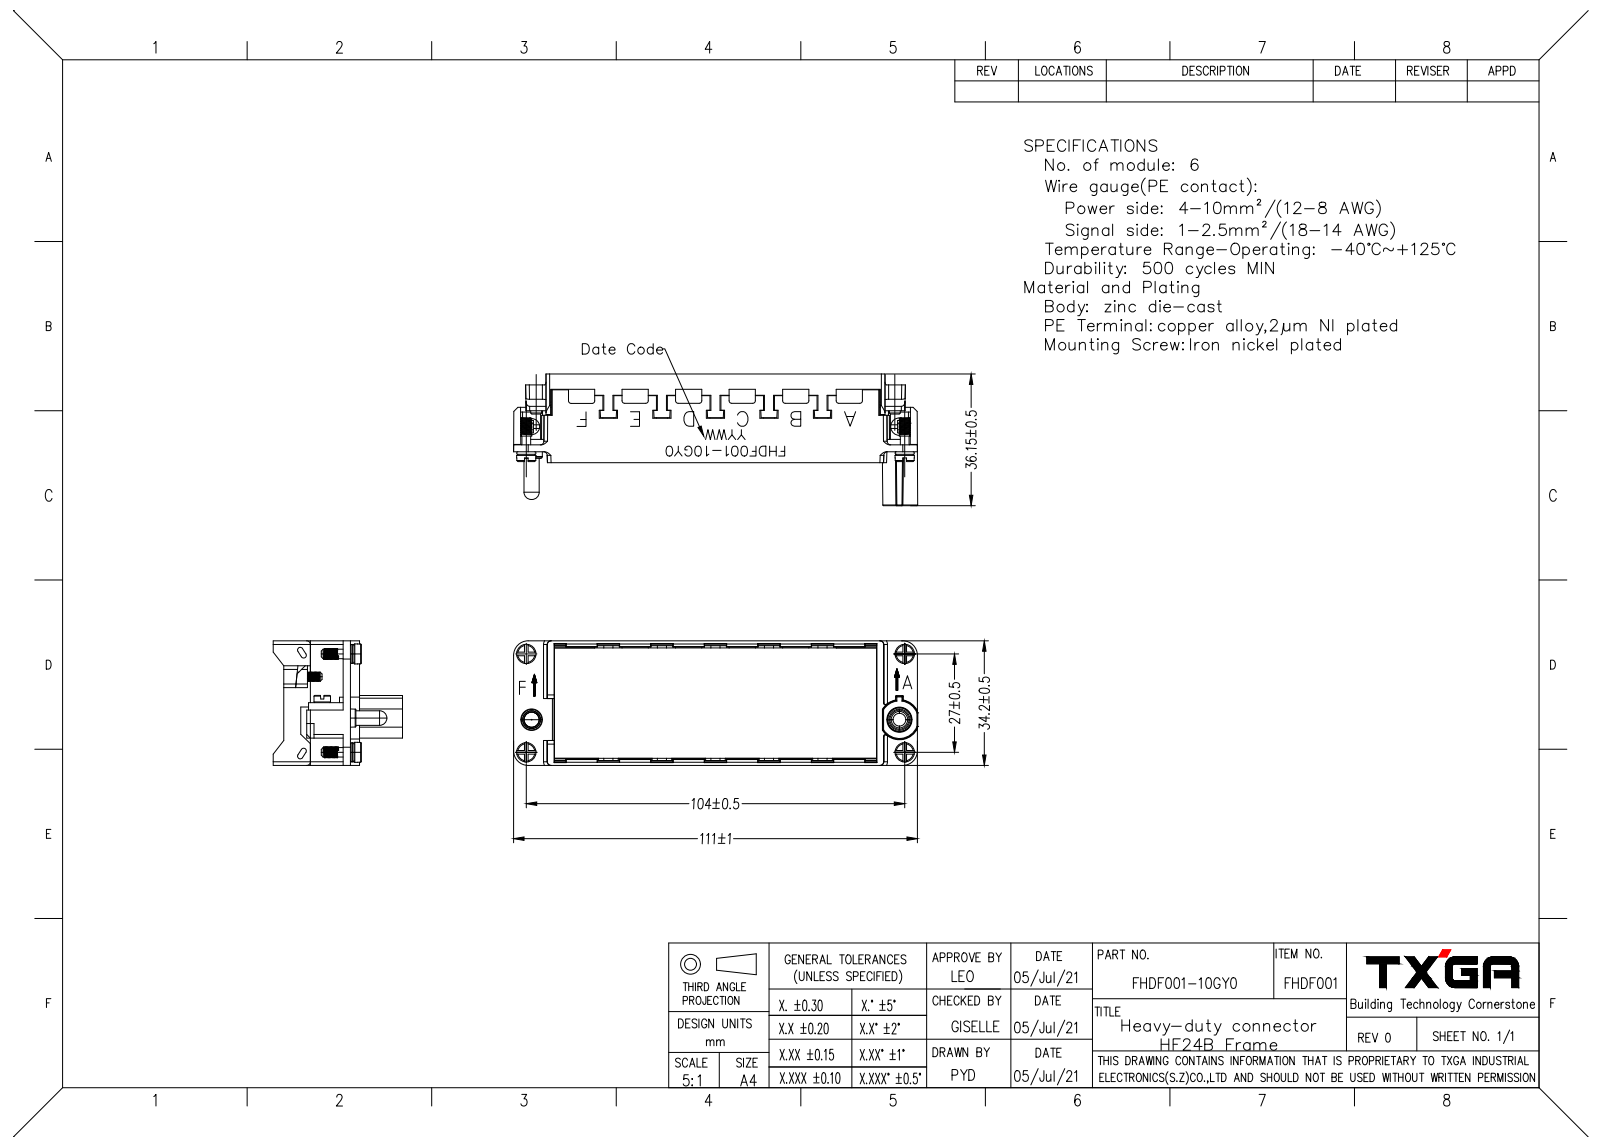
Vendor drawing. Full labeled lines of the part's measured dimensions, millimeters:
Part name (STEP PRODUCT): FHDF001-10NA0 HF24B-NUA-REF（渲染）
STEP written by: SolidWorks 2021 (CONFIG_CONTROL_DESIGN)
Units: millimetres
Bodies: 1 solid, 1193 faces (656 planar, 387 cylindrical, 150 other)
Overall size (bounding box): 111 × 35.5 × 34.2
Volume: 13 326 mm³ · Surface area: 17 658 mm²
Round holes (diameter × count): ⌀3 ×4, ⌀3.2 ×4, ⌀4.36 ×2, ⌀4.69 ×1, ⌀6.5 ×1
Round bosses / shafts (diameter × count): ⌀5.5 ×4, ⌀5.2 ×4, ⌀2.6 ×4, ⌀2.5 ×4, ⌀4.53 ×2, ⌀5.69 ×1, ⌀4 ×1
Partial cylindrical surfaces — rounded edges, fillets, slot ends (radius × count): R1 ×28, R0.5 ×14, R0.4 ×4, R0.74 ×4, R5 ×4, R3.46 ×2, R3.5 ×2, R4 ×2
Main face-to-face distances: 1.75, 32.45, 34.2, 30.7, 2.3, 90.7, 31.3, 0.6, 88.4, 2
Hole centre spacings: 9.5, 17.66, 27, 103.03, 104, 104.1, 107.45, 101.2
